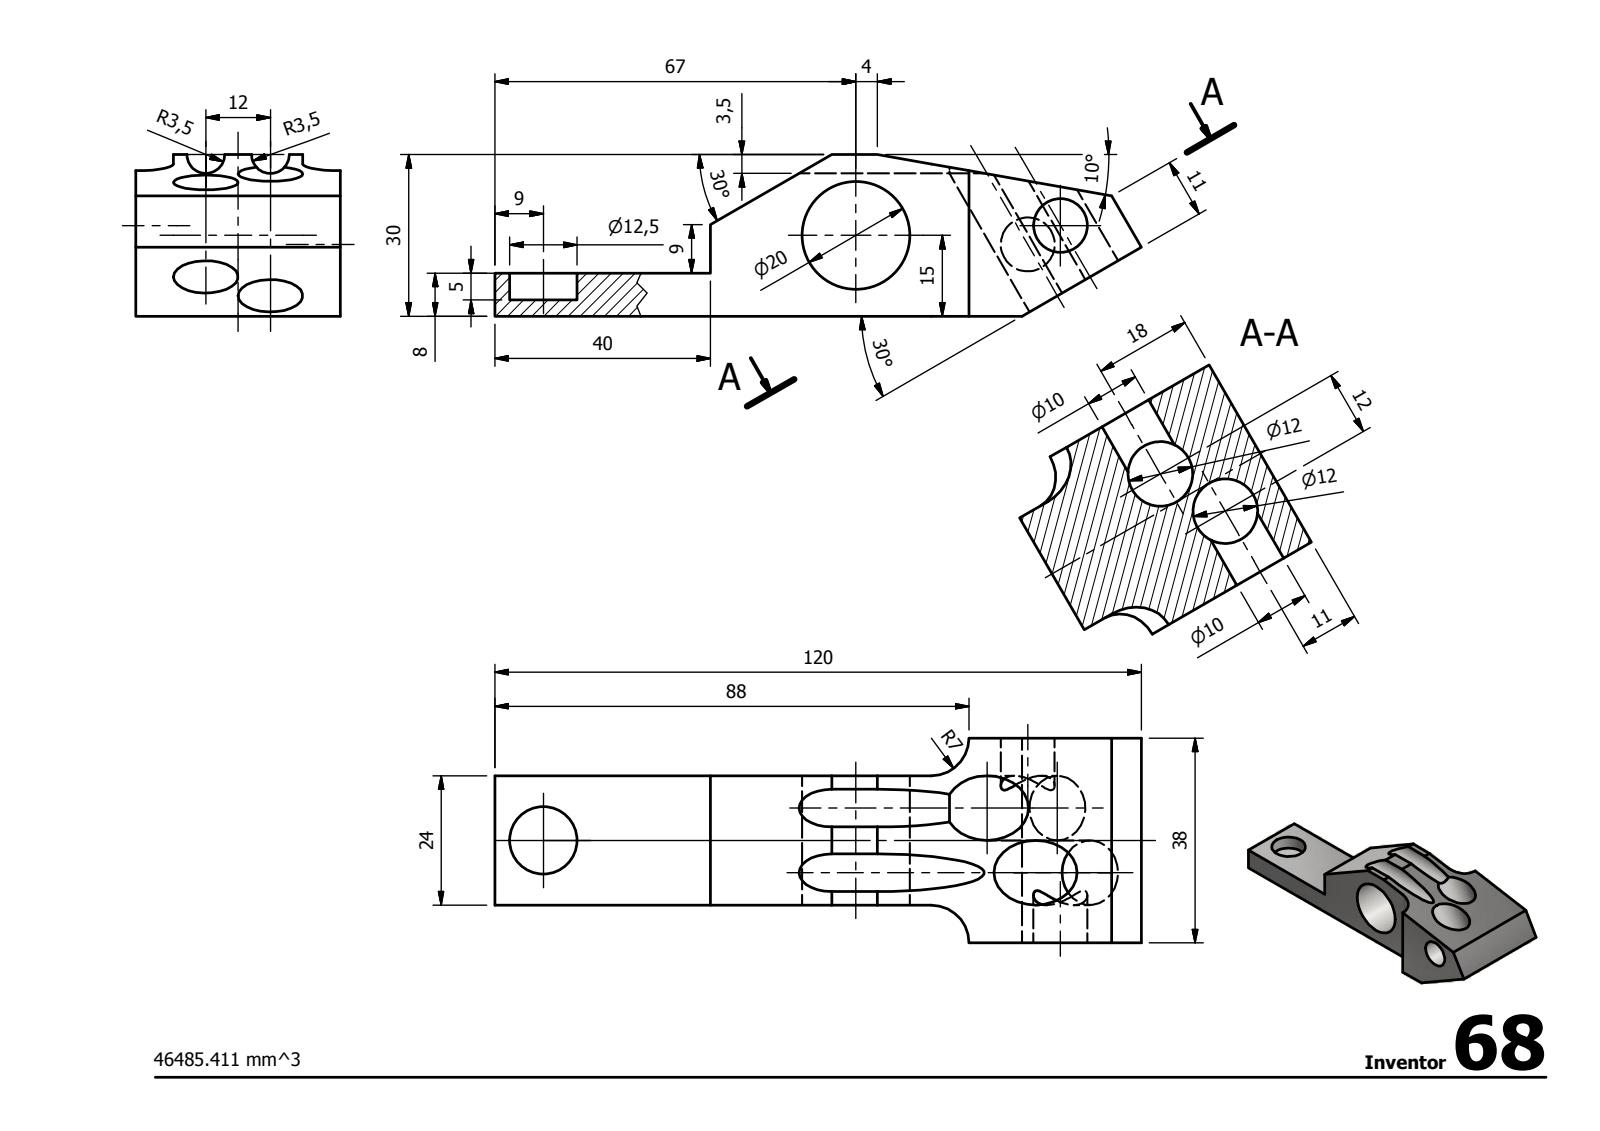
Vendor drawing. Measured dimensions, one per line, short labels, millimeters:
written by: Autodesk Inventor 2014 (AUTOMOTIVE_DESIGN)
unit: mm
bodies: 1 solid, 26 faces (16 planar, 10 cylindrical, 0 other)
size: 120 × 38 × 30
volume: 46 483 mm³; area: 14 775 mm²
holes: 2× ⌀10, 2× ⌀12, 1× ⌀12.5, 1× ⌀20
rounds: 2× R3.5, 2× R7
face distances: 24, 7, 31, 8, 43.63, 38, 40, 3, 5, 30
hole spacings: 7, 13.9, 31.95, 38.01
